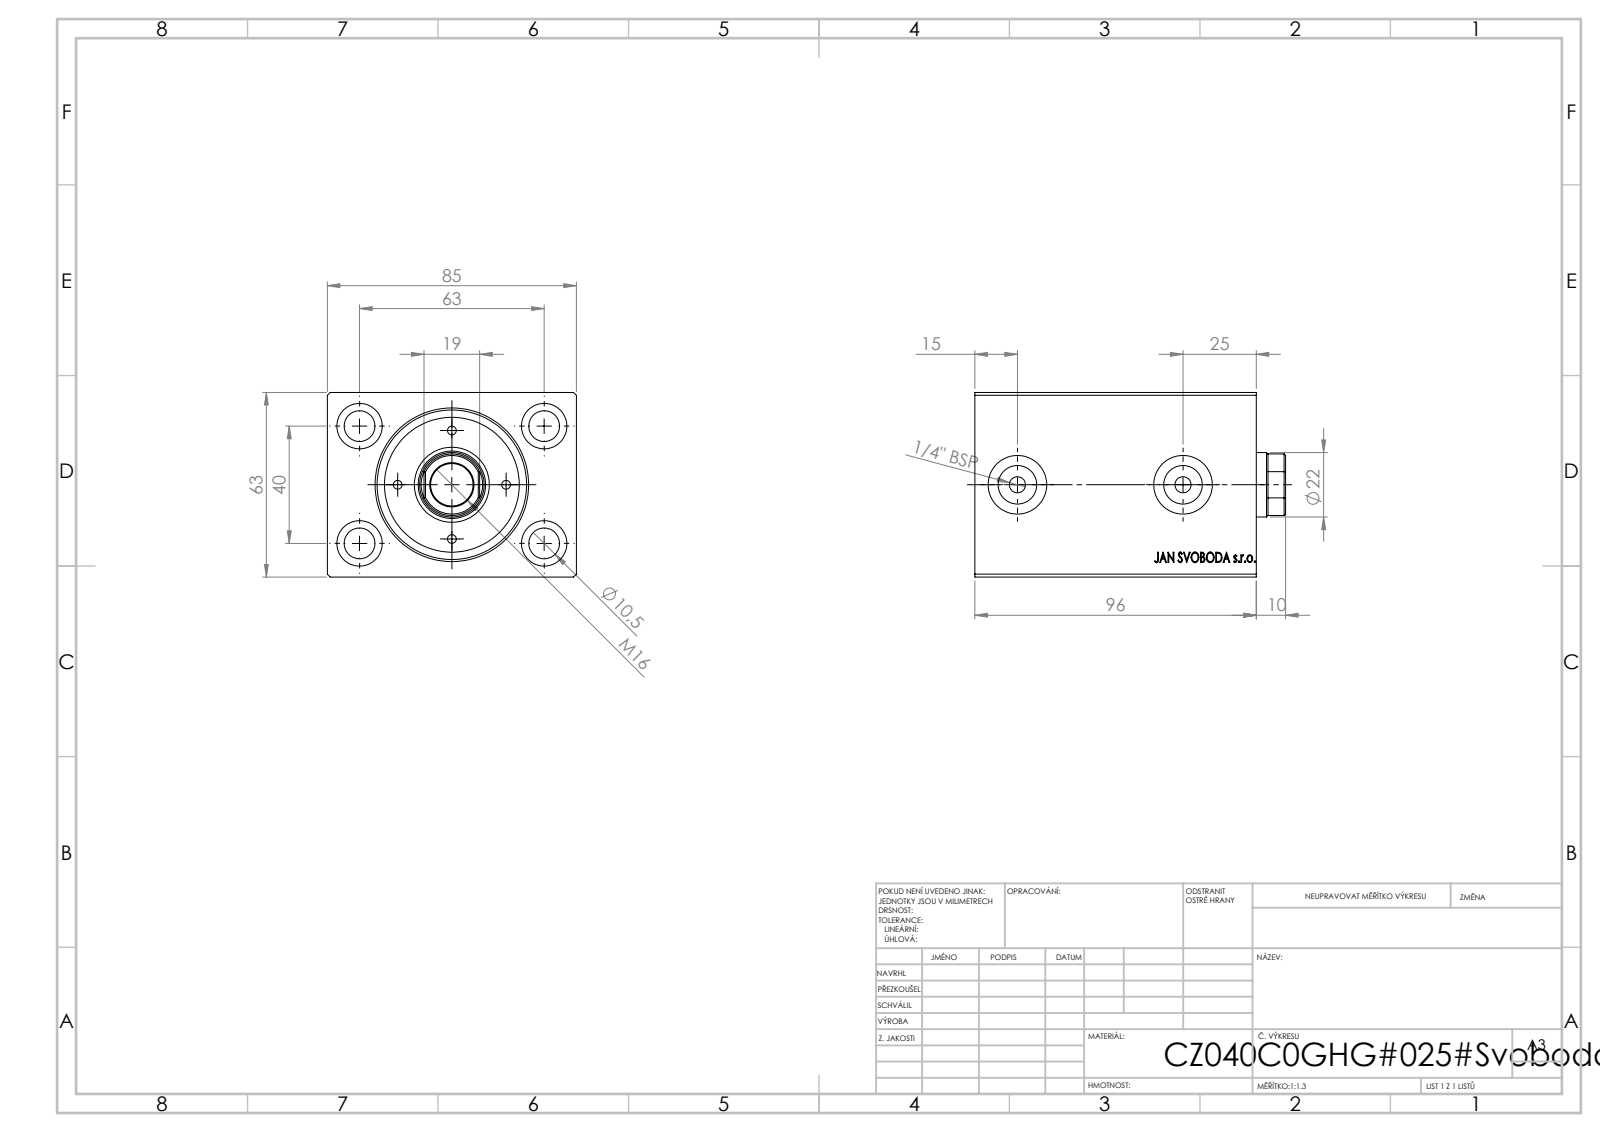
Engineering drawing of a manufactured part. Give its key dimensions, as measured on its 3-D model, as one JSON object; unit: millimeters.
{"step_written_by": "SolidWorks 2019 (CONFIG_CONTROL_DESIGN)", "units": "millimeters", "bodies": {"solids": 1, "faces": 825, "planar": 397, "cylindrical": 46, "other": 382}, "overall_size": [96, 85, 63], "volume_mm3": 358504, "surface_area_mm2": 64185, "round_holes": [[10.5, 4], [15.5, 4], [5.5, 2], [8, 2], [13.16, 2], [20, 2], [36, 1], [40, 1], [51, 1]], "face_to_face_distances": [63, 85, 96, 80.7, 15.3, 95.8, 15.1, 10.33, 85.67, 10], "hole_center_spacings": [37.31, 40, 63, 74.63, 36.5, 56.5]}
